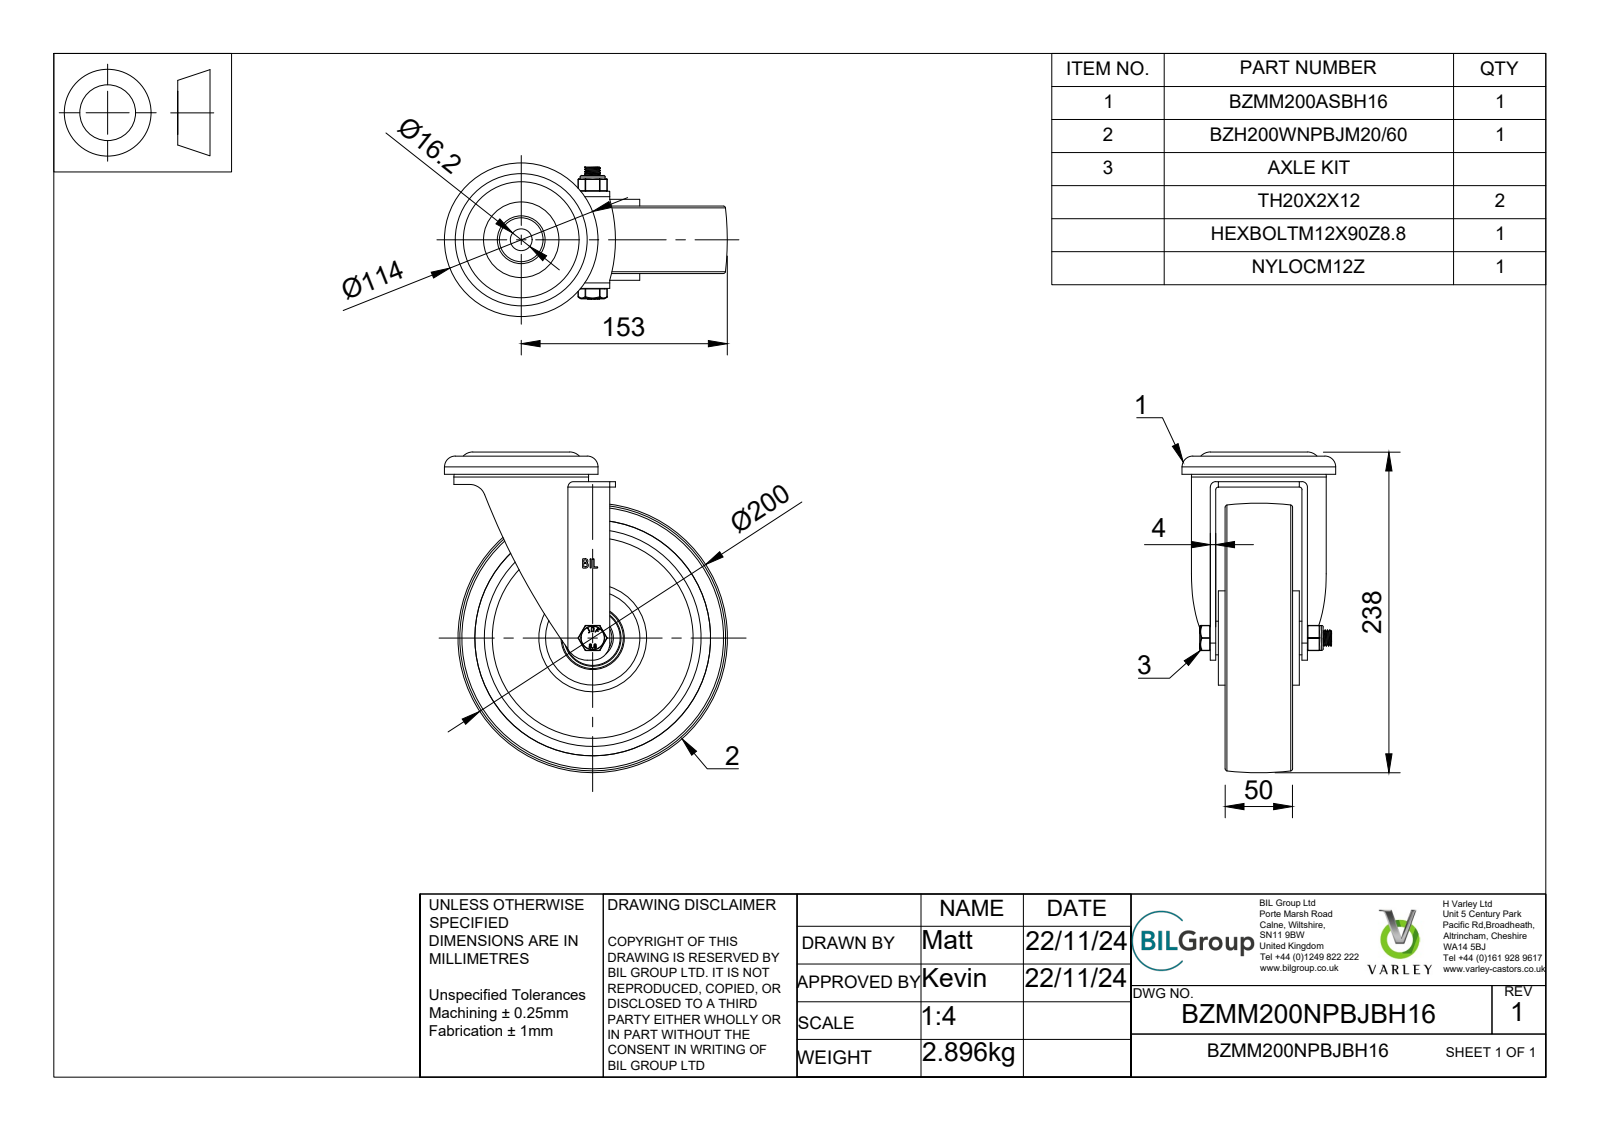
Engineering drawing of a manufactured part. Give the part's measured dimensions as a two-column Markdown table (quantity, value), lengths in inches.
| quantity | value |
| --- | --- |
| part name | BZMM200NPBJBH16 v3; BZMM200ASBH16 - 64 v1; ZINC PLATED, PRESSED STEEL HEAD; ZINC PLATED, PRESSED STEEL FORKS (+7 more) |
| STEP written by | Autodesk Translation Framework v13.20.0.188 (AP242_MANAGED_MODEL_BASED_3D_ENGINEERING_MIM_LF) |
| units | inches |
| bodies | 36 solids, 1113 faces (467 planar, 207 cylindrical, 439 other) |
| overall size | 9.37 × 8.268 × 4.488 |
| volume | 63.77 in³ |
| surface area | 511.5 in² |
| round holes (diameter × count) | 0.472 × 1, 0.48 × 1, 0.551 × 1, 0.638 × 1, 0.787 × 1, 1.122 × 1, 1.213 × 1, 1.575 × 1, 1.587 × 1, 1.594 × 1, 1.614 × 1, 1.654 × 1 |
| round bosses / shafts (diameter × count) | 4.488 × 1, 3.937 × 1, 2.913 × 1, 2.756 × 1, 1.85 × 1, 1.606 × 1, 1.28 × 1, 1.232 × 1 |
| partial cylindrical surfaces (radius × count) | 0.02 × 19, 0.019 × 4, 0.035 × 4, 0.079 × 4, 0.035 × 2, 0.035 × 2, 0.157 × 2, 0.267 × 2 |
| main face-to-face distances | 0.236, 0.866, 1.102, 1.299, 0.157, 1.969, 0.276, 1.142, 1.378, 2.244 |
